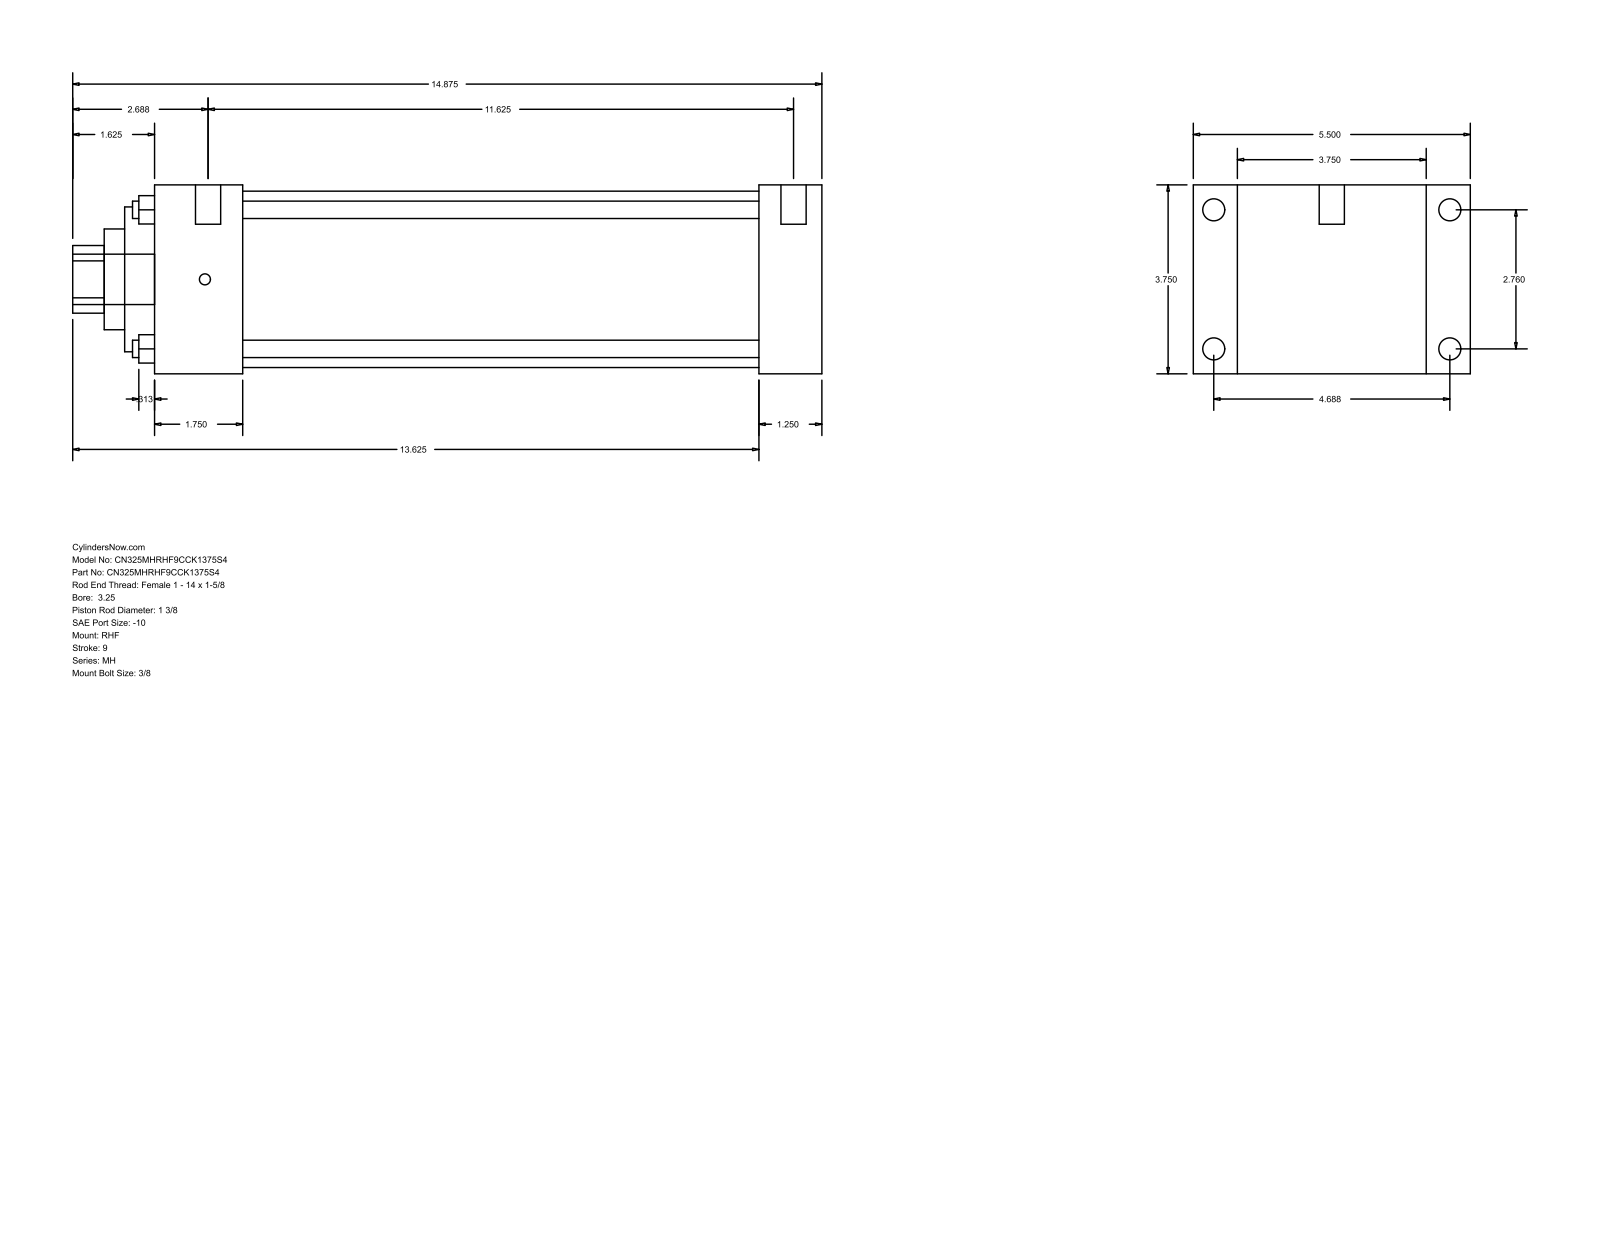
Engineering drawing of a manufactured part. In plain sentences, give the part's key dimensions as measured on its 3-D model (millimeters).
The part is named "MH_RHF__0325_1.375". Its 3-D file was written by "GSSL Pune (CONFIG_CONTROL_DESIGN)". It is 0 solids with 90 faces: 61 planar, 29 cylindrical and 0 other. Overall it measures 377.82 by 139.7 by 95.25 millimeters. Round holes: 4 of diameter 8.76, 1 of diameter 34.92, 1 of diameter 50.8, 1 of diameter 73.03, 1 of diameter 88.9. Round bosses or shafts: 4 of diameter 11.13, 4 of diameter 5.56, 2 of diameter 12.7, 1 of diameter 25.4. Partial cylindrical surfaces (rounded edges, fillets, slot ends): 1 of radius 17.06. The main face-to-face distances are 95.24, 31.75, 22.23, 117.47, 304.8, 336.55, 139.7, 44.45, 260.35, 292.1. The hole center spacings are 49.57, 70.1, 99.14.
